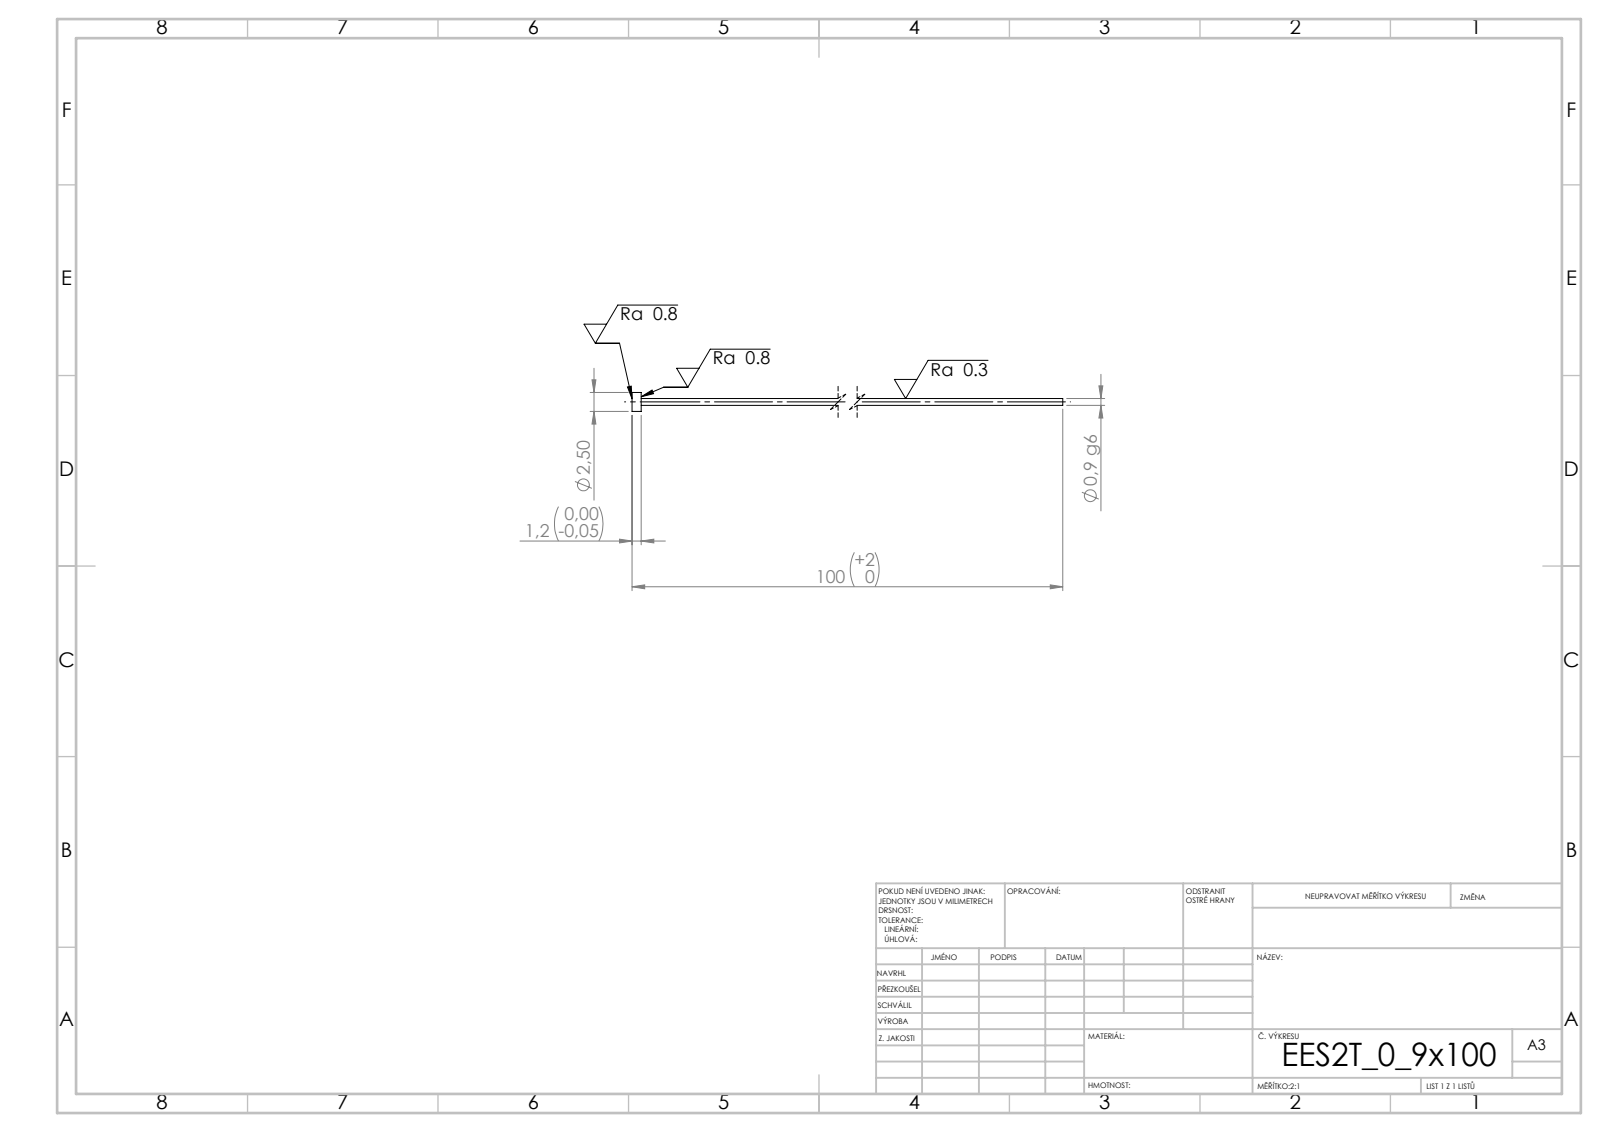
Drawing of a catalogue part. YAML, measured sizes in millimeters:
step_written_by: "SolidWorks 2019 (CONFIG_CONTROL_DESIGN)"
units: millimeters
bodies: {solids: 1, faces: 7, planar: 3, cylindrical: 4, other: 0}
overall_size: [100, 2.5, 2.5]
volume: 69
surface_area: 299
round_bosses_or_shafts:
  - {diameter: 2.5, count: 1}
  - {diameter: 0.9, count: 1}
face_to_face_distances: [1.2, 100, 98.8]
